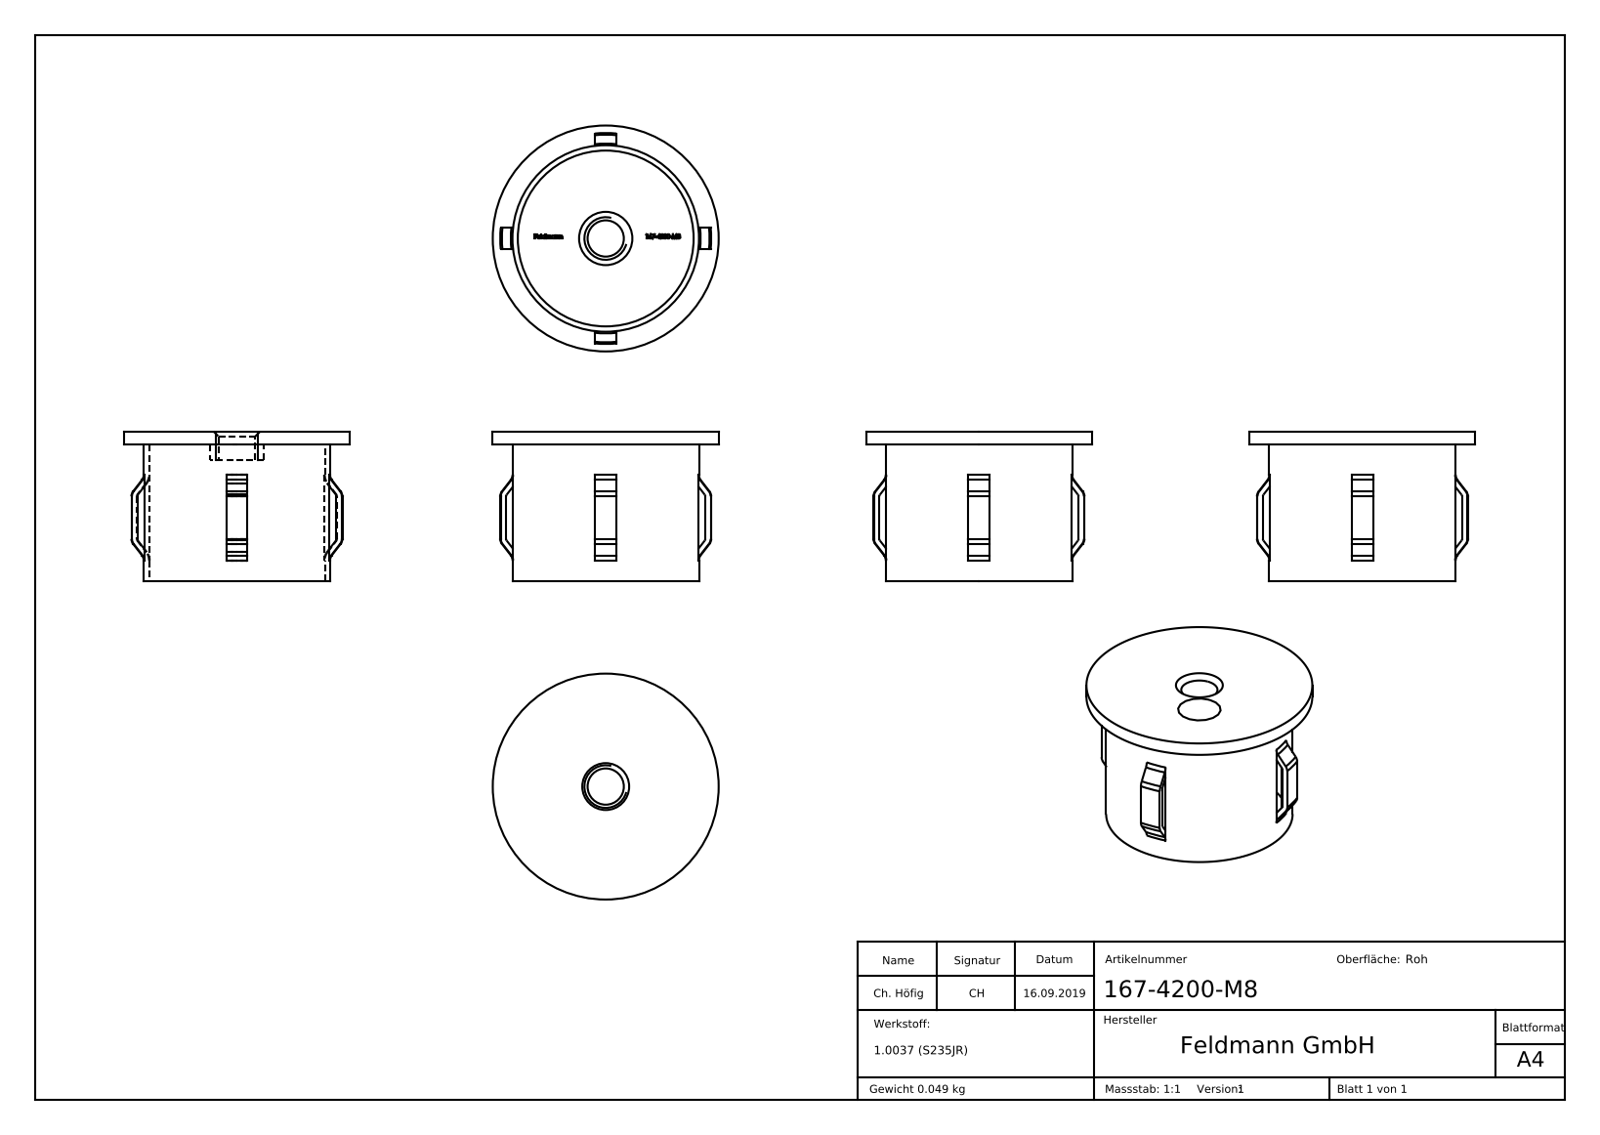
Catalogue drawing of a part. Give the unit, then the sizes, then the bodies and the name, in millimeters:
Units: millimetres
Overall size (bounding box): 42.4 × 42.4 × 28.2
Round holes (diameter × count): ⌀6.8 ×1, ⌀33 ×1
Round bosses / shafts (diameter × count): ⌀42.4 ×1, ⌀35 ×1, ⌀10 ×1
Partial cylindrical surfaces — rounded edges, fillets, slot ends (radius × count): R18.8 ×1, R19.8 ×1
Main face-to-face distances: 2.5, 4, 25.7, 28.2, 22.9, 2.8, 5.3, 2.4, 25.8, 2.9
Volume: 6 313 mm³ · Surface area: 9 039 mm²
Bodies: 1 solid, 338 faces (158 planar, 20 cylindrical, 160 other)
Part name (STEP PRODUCT): 167-4200-M8
STEP written by: SolidWorks 2015 (CONFIG_CONTROL_DESIGN)
